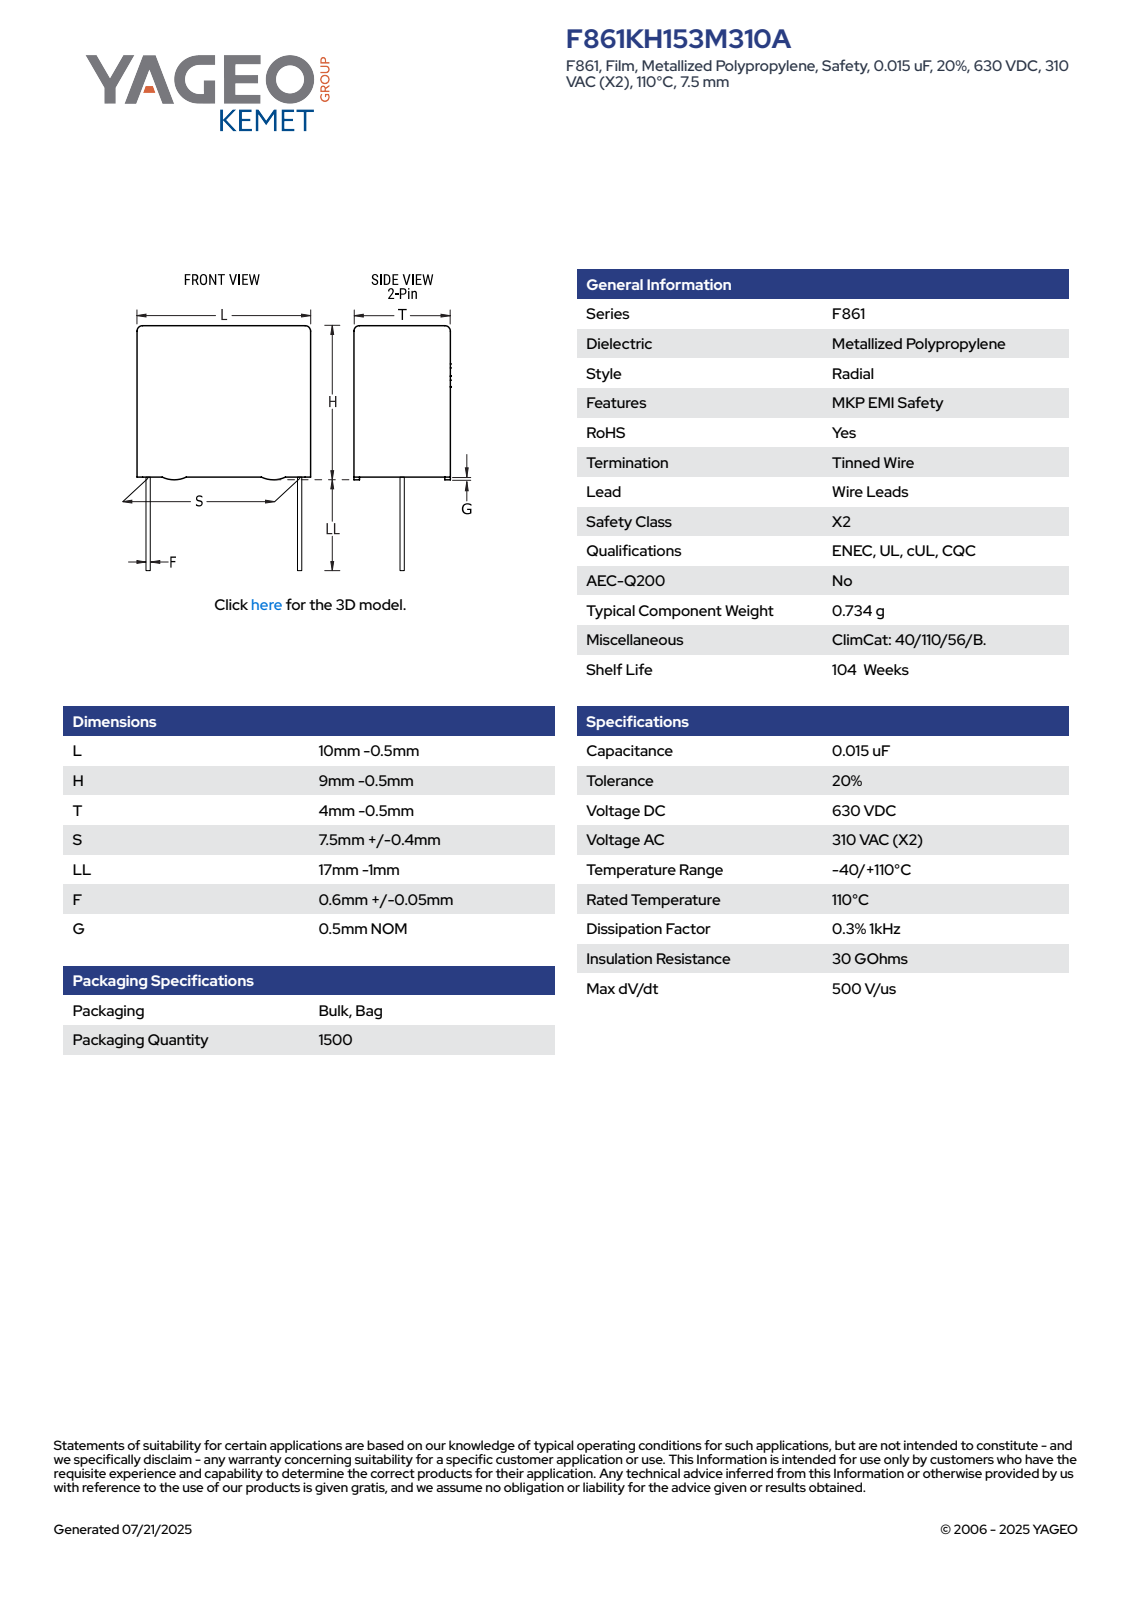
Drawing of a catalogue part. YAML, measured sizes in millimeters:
part_name: "CFR_RBG_10X9X4_L9.5H8.5T3.5S7.5LL16F0.65G0.5"
step_written_by: "SolidWorks 2014 (AUTOMOTIVE_DESIGN)"
units: millimeters
bodies: {solids: 4, faces: 89, planar: 81, cylindrical: 8, other: 0}
overall_size: [24.5, 9.5, 3.5]
volume: 276
surface_area: 353
round_bosses_or_shafts:
  - {diameter: 0.65, count: 2}
partial_cylinders:
  - {radius: 0.5, count: 4}
face_to_face_distances: [3.5, 9.5, 8, 3.3, 3.1, 0.5, 8.5, 16, 16.5, 24.5]
